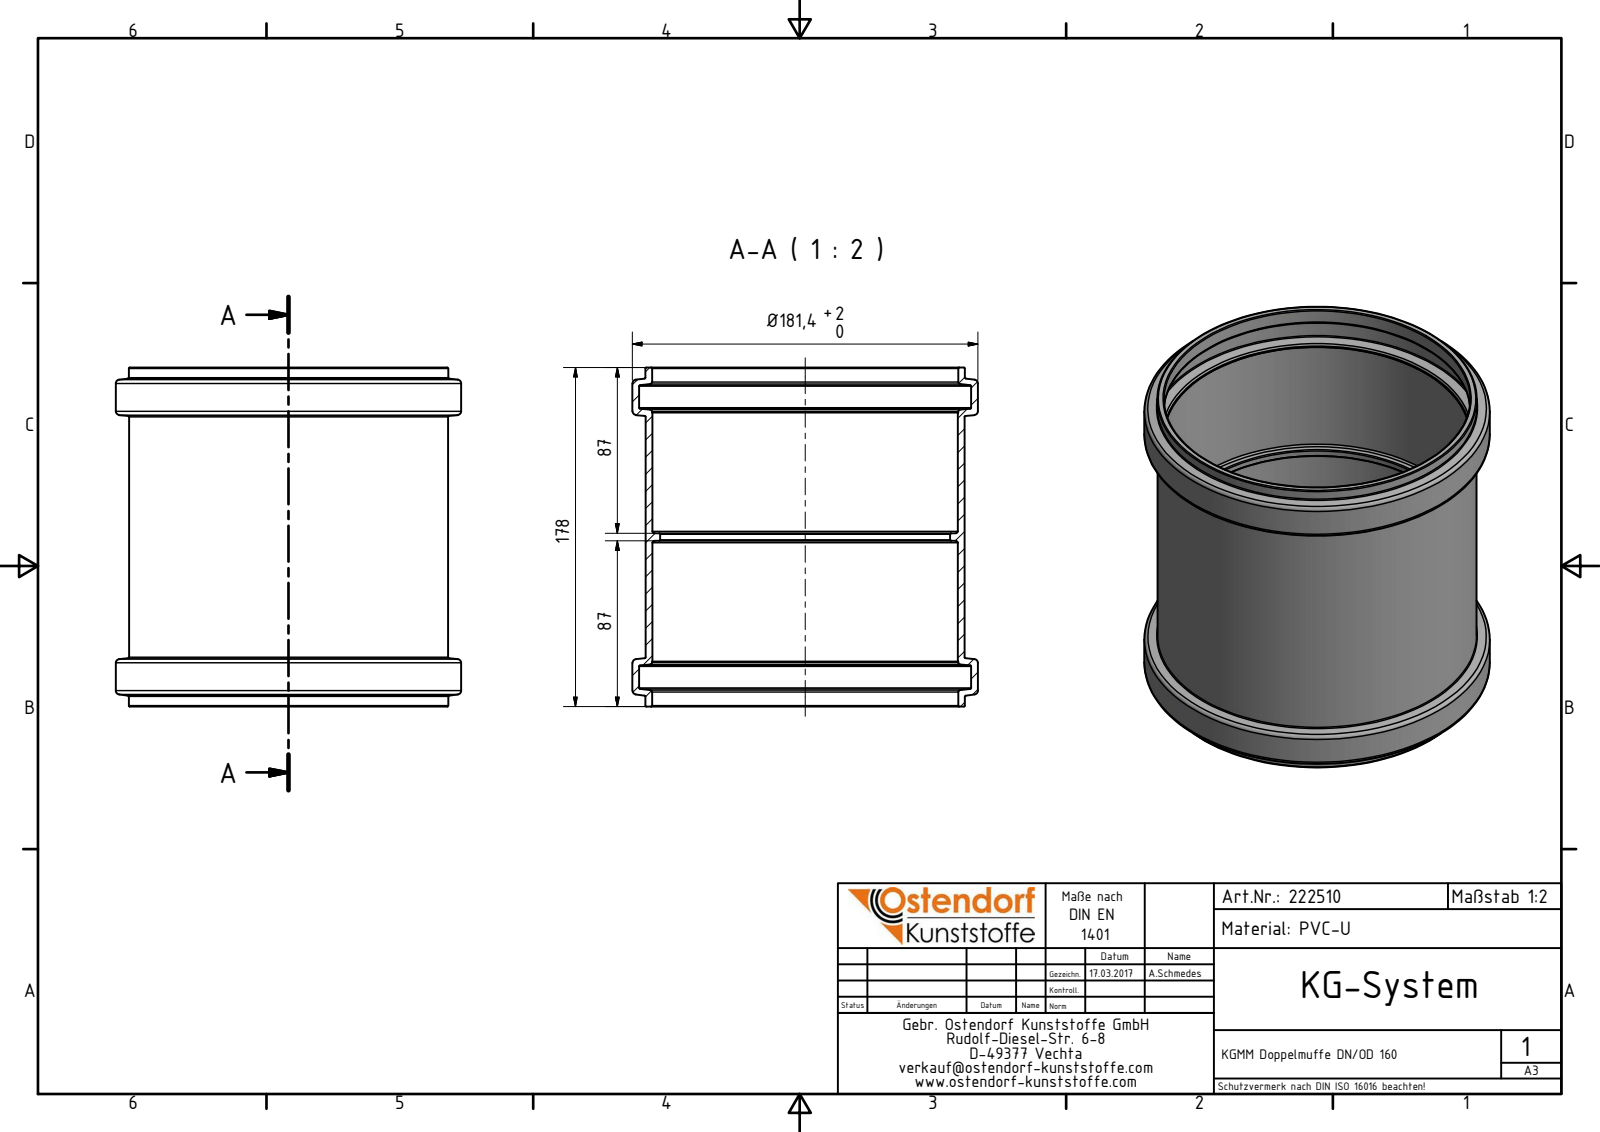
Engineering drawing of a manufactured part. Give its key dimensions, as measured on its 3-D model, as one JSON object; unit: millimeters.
{"part_name": "222510 KGMM Doppelmuffe DN_OD 160", "step_written_by": "Autodesk Inventor 2016 (AUTOMOTIVE_DESIGN)", "units": "millimeters", "bodies": {"solids": 1, "faces": 52, "planar": 6, "cylindrical": 14, "other": 32}, "overall_size": [181.4, 181.4, 178], "volume_mm3": 376497, "surface_area_mm2": 216394, "round_holes": [[152.3, 1], [160.5, 1], [160.8, 1], [174.4, 1]], "round_bosses_or_shafts": [[181.4, 1], [167.8, 1], [167.5, 1]], "face_to_face_distances": [87, 91, 178, 4, 23.63, 154.37, 63.37, 67.37, 130.74]}
